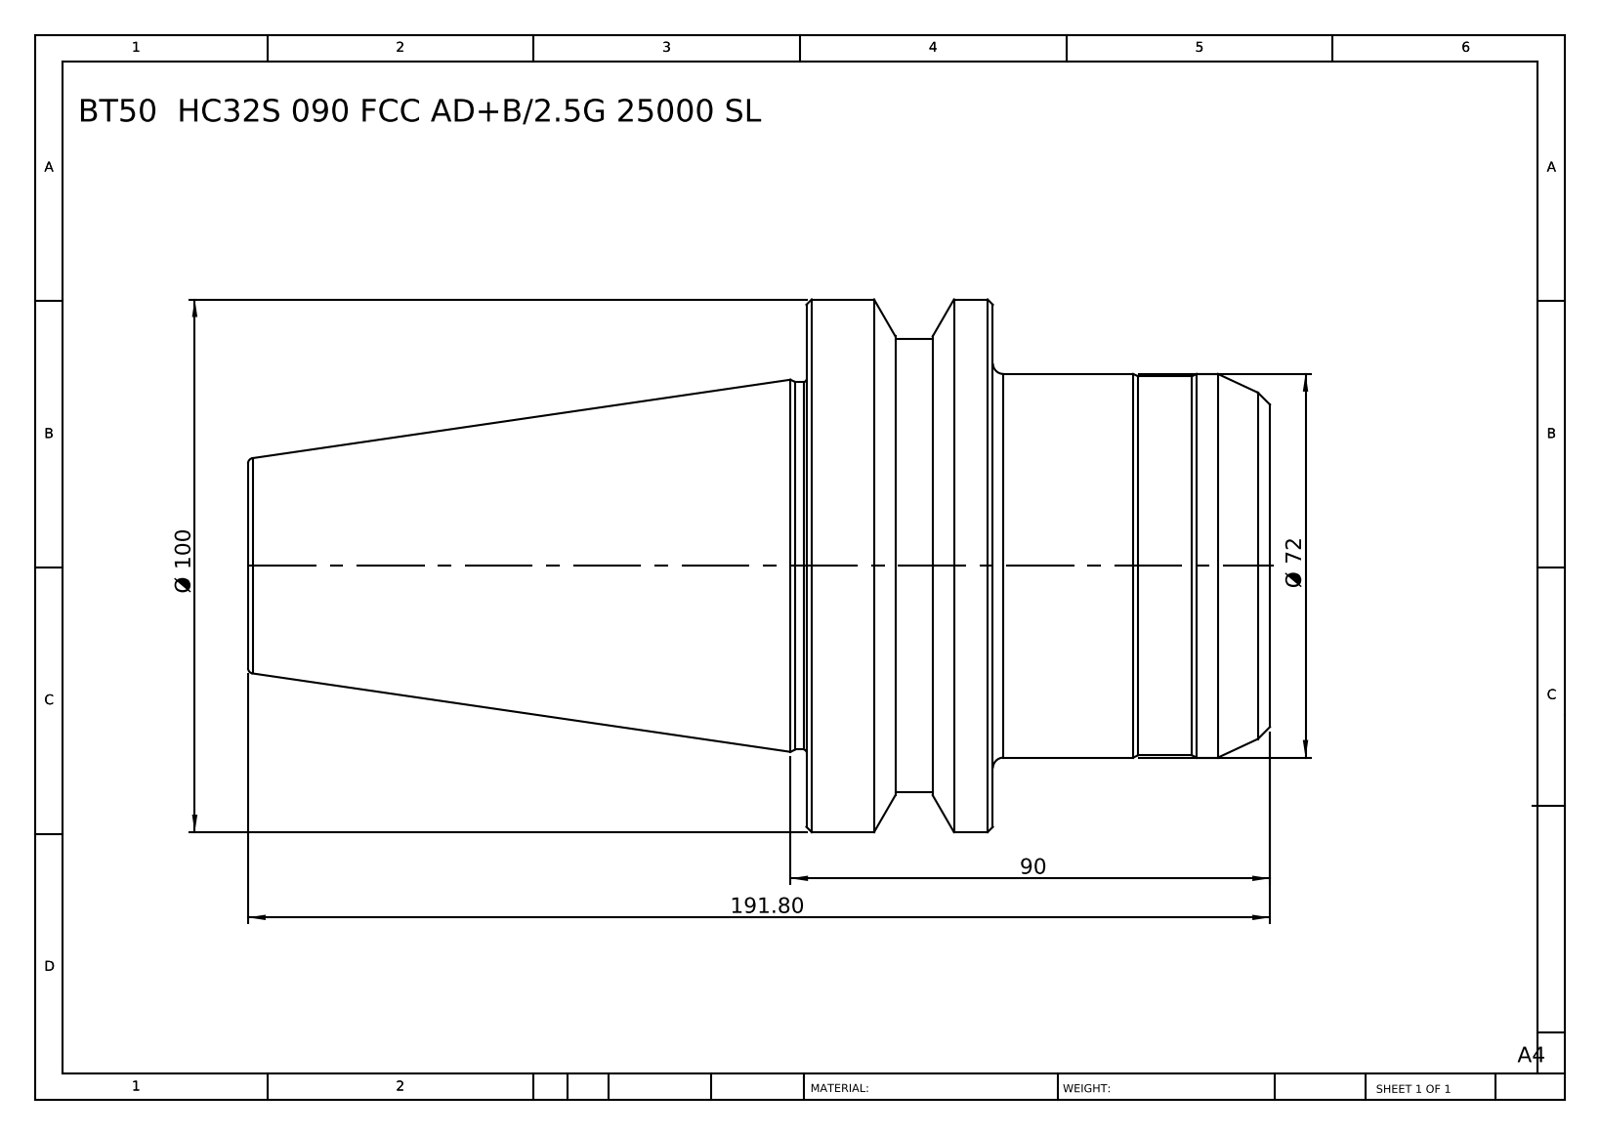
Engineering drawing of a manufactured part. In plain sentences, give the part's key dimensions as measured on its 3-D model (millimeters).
The part is named "BT50 HC32S 090 FCC AD+B-2.5G 25000 SL". Its 3-D file was written by "SolidWorks 2014 (CONFIG_CONTROL_DESIGN)". It is 1 solid with 46 faces: 6 planar, 14 cylindrical and 26 other. Overall it measures 191.8 by 100 by 100 millimeters. Its volume is 715 770 cubic millimeters and its surface area 54 957 square millimeters. Round bosses or shafts: 1 of diameter 100, 1 of diameter 85, 1 of diameter 72, 1 of diameter 71.1, 1 of diameter 69. The main face-to-face distances are 35, 52, 87, 191.8, 139.8, 104.8, 63.3, 11.3, 23.7, 128.5.
